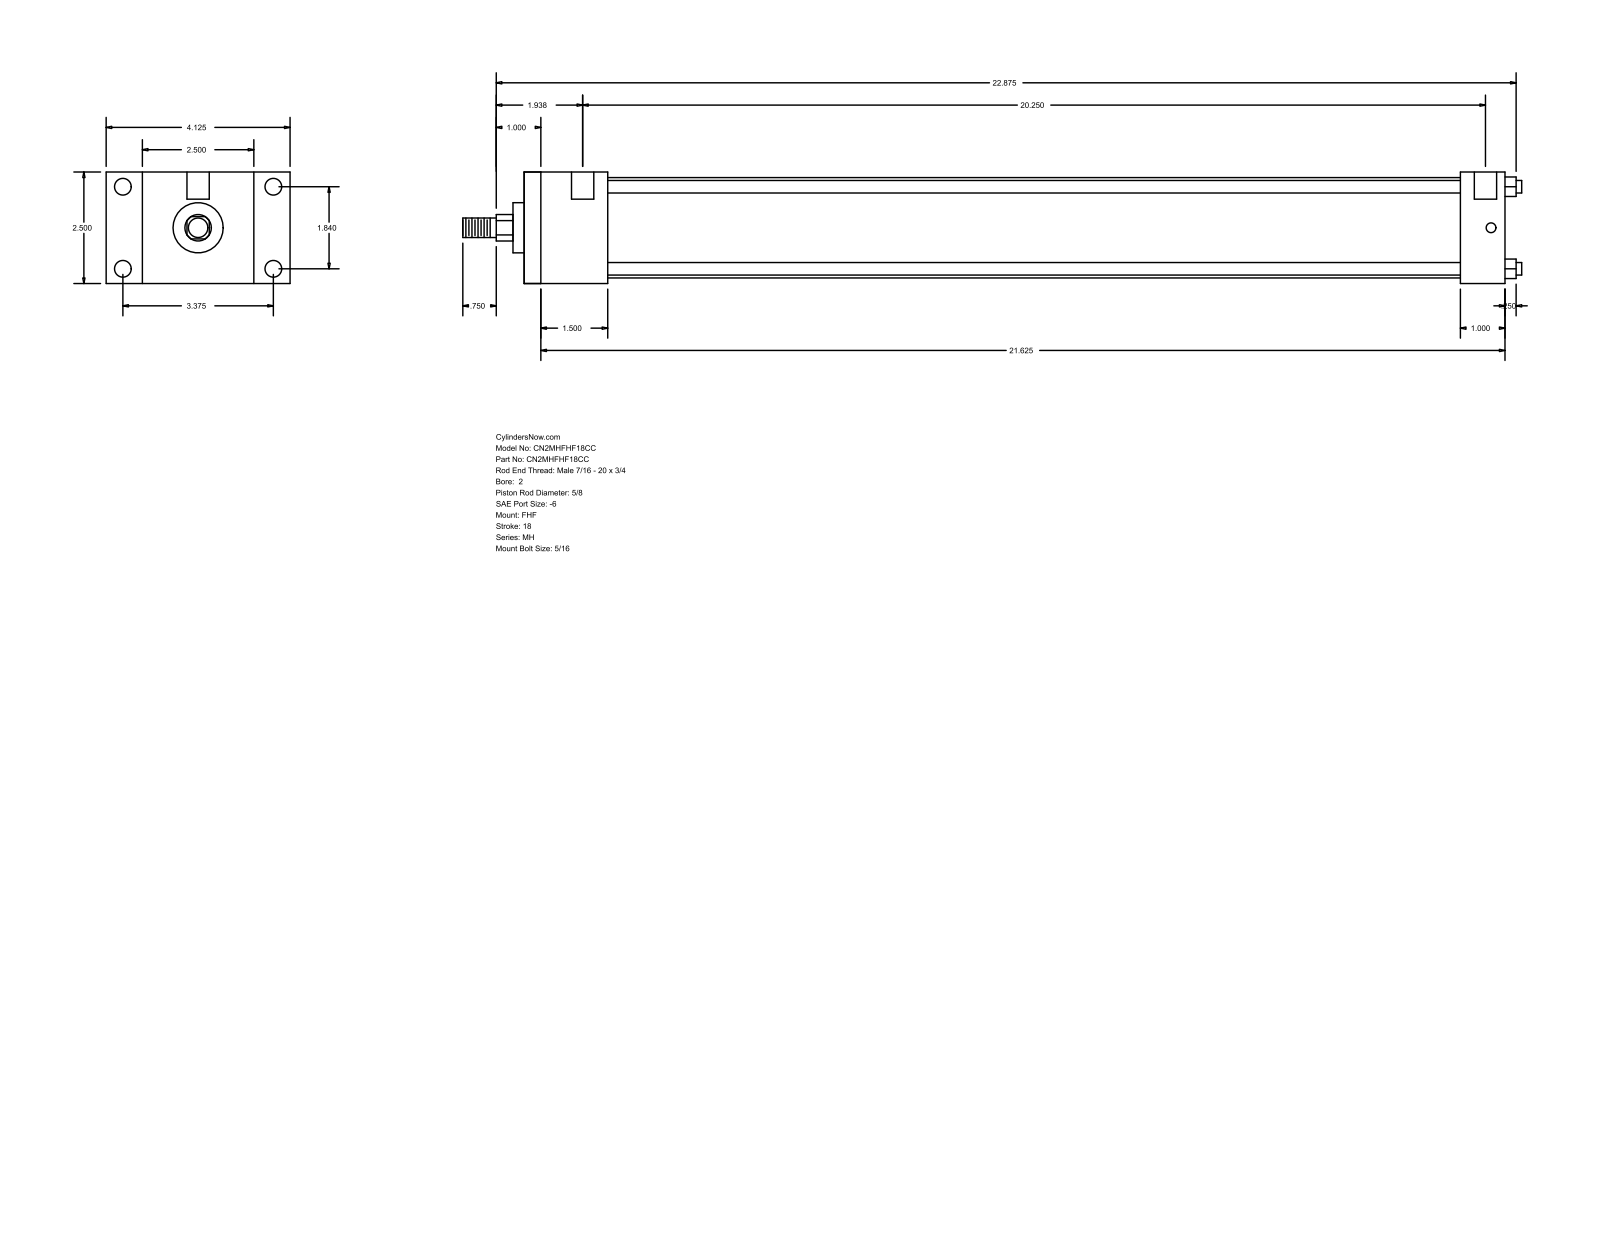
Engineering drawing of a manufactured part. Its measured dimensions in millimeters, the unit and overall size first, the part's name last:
Units: millimetres
Overall size (bounding box): 603.25 × 104.78 × 63.5
Round holes (diameter × count): ⌀5.56 ×4, ⌀9.53 ×4, ⌀12.7 ×2
Round bosses / shafts (diameter × count): ⌀7.14 ×4, ⌀57.15 ×1, ⌀28.57 ×1, ⌀15.88 ×1, ⌀11.11 ×1
Partial cylindrical surfaces — rounded edges, fillets, slot ends (radius × count): R7.54 ×1
Main face-to-face distances: 63.5, 47.62, 558.79, 511.17, 20.64, 84.14, 104.78, 25.4, 533.39, 485.77
Hole centre spacings: 46.74, 85.72, 97.63, 522.29, 3.18, 4.76, 514.35, 517.53
Bodies: 0 solids, 88 faces (60 planar, 28 cylindrical, 0 other)
Part name (STEP PRODUCT): MH_FHF__0200_0.625
STEP written by: GSSL Pune (CONFIG_CONTROL_DESIGN)
